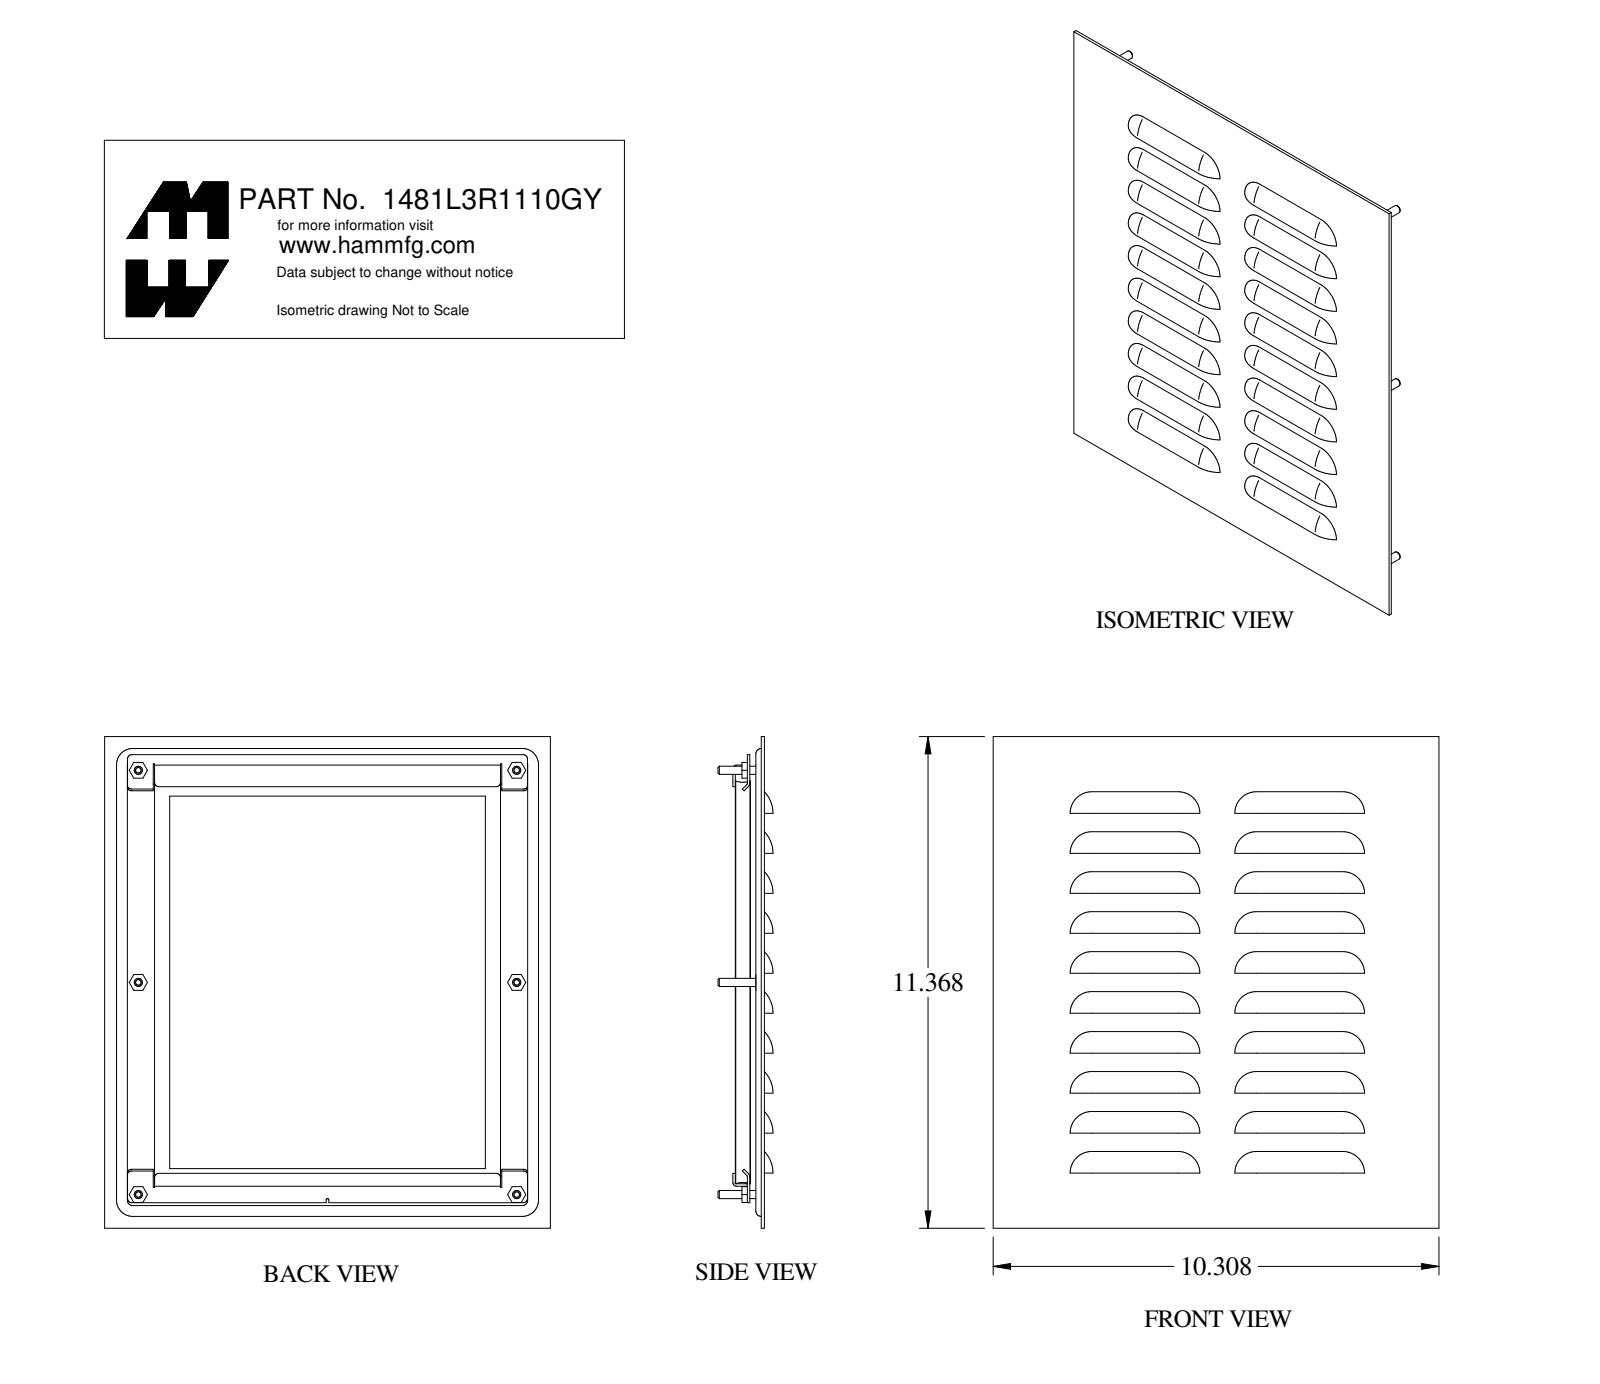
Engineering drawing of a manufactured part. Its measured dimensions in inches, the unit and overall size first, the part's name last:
Units: inches
Overall size (bounding box): 11.368 × 10.308 × 1.272
Round holes (diameter × count): ⌀0.156 ×6, ⌀0.22 ×4
Round bosses / shafts (diameter × count): ⌀0.25 ×6, ⌀0.188 ×6
Partial cylindrical surfaces — rounded edges, fillets, slot ends (radius × count): R0.1 ×12, R0.653 ×10, R0.725 ×10, R0.029 ×6, R0.086 ×6, R0.125 ×4, R0.126 ×4, R0.374 ×4
Main face-to-face distances: 0.072, 0.3, 0.25, 0.372, 0.622, 0.55, 0.05, 0.322, 0.6, 0.672
Hole centre spacings: 4.905, 9.81, 10.031, 13.145, 8.75, 8.75, 10.031, 13.146
Volume: 30.41 in³ · Surface area: 507.3 in²
Bodies: 17 solids, 432 faces (197 planar, 131 cylindrical, 104 other)
Part name (STEP PRODUCT): 1481L3R1110GY
STEP written by: SolidWorks 2021 (AUTOMOTIVE_DESIGN)
